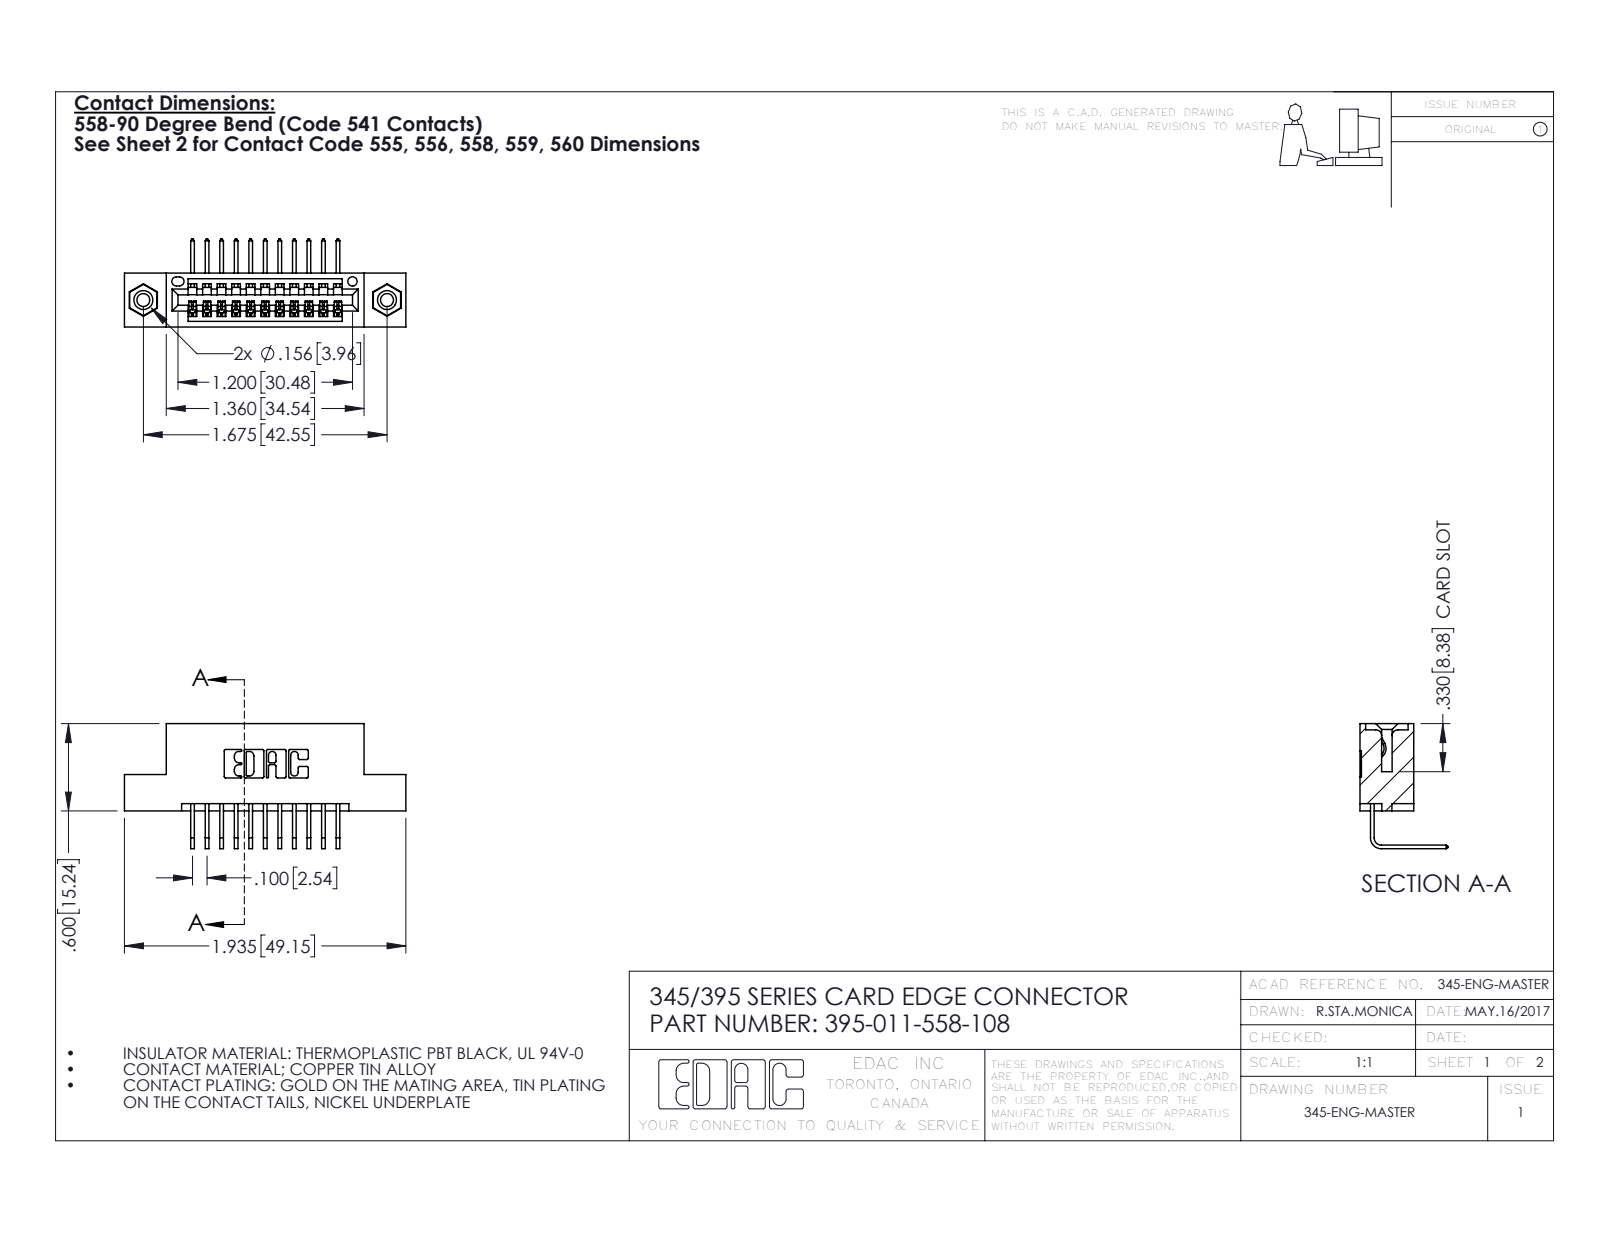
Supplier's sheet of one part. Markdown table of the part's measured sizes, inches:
| quantity | value |
| --- | --- |
| part name | 345-250-001_345-250-003-102; 345-292-001_558 Tail - 2; 345 Part_Flush Mounting Lugs - 0.156 Dia-TI; 395-011-558-108 |
| STEP written by | SolidWorks 2016 (CONFIG_CONTROL_DESIGN) |
| units | inches |
| bodies | 14 solids, 846 faces (574 planar, 256 cylindrical, 16 other) |
| overall size | 1.935 × 0.859 × 0.605 |
| volume | 0.271 in³ |
| surface area | 8.865 in² |
| round holes (diameter × count) | 0.089 × 2, 0.125 × 2, 0.156 × 2, 0.064 × 1 |
| round bosses / shafts (diameter × count) | 0.155 × 2 |
| partial cylindrical surfaces (radius × count) | 0.006 × 22, 0.01 × 22, 0.007 × 6, 0.031 × 6, 0.026 × 3, 0.031 × 2, 0.04 × 2, 0.014 × 1 |
| main face-to-face distances | 0.2, 0.072, 0.298, 0.37, 0.098, 0.272, 0.025, 0.1, 0.6, 0.06 |
| hole center spacings | 0.27, 1.443, 1.675 |
